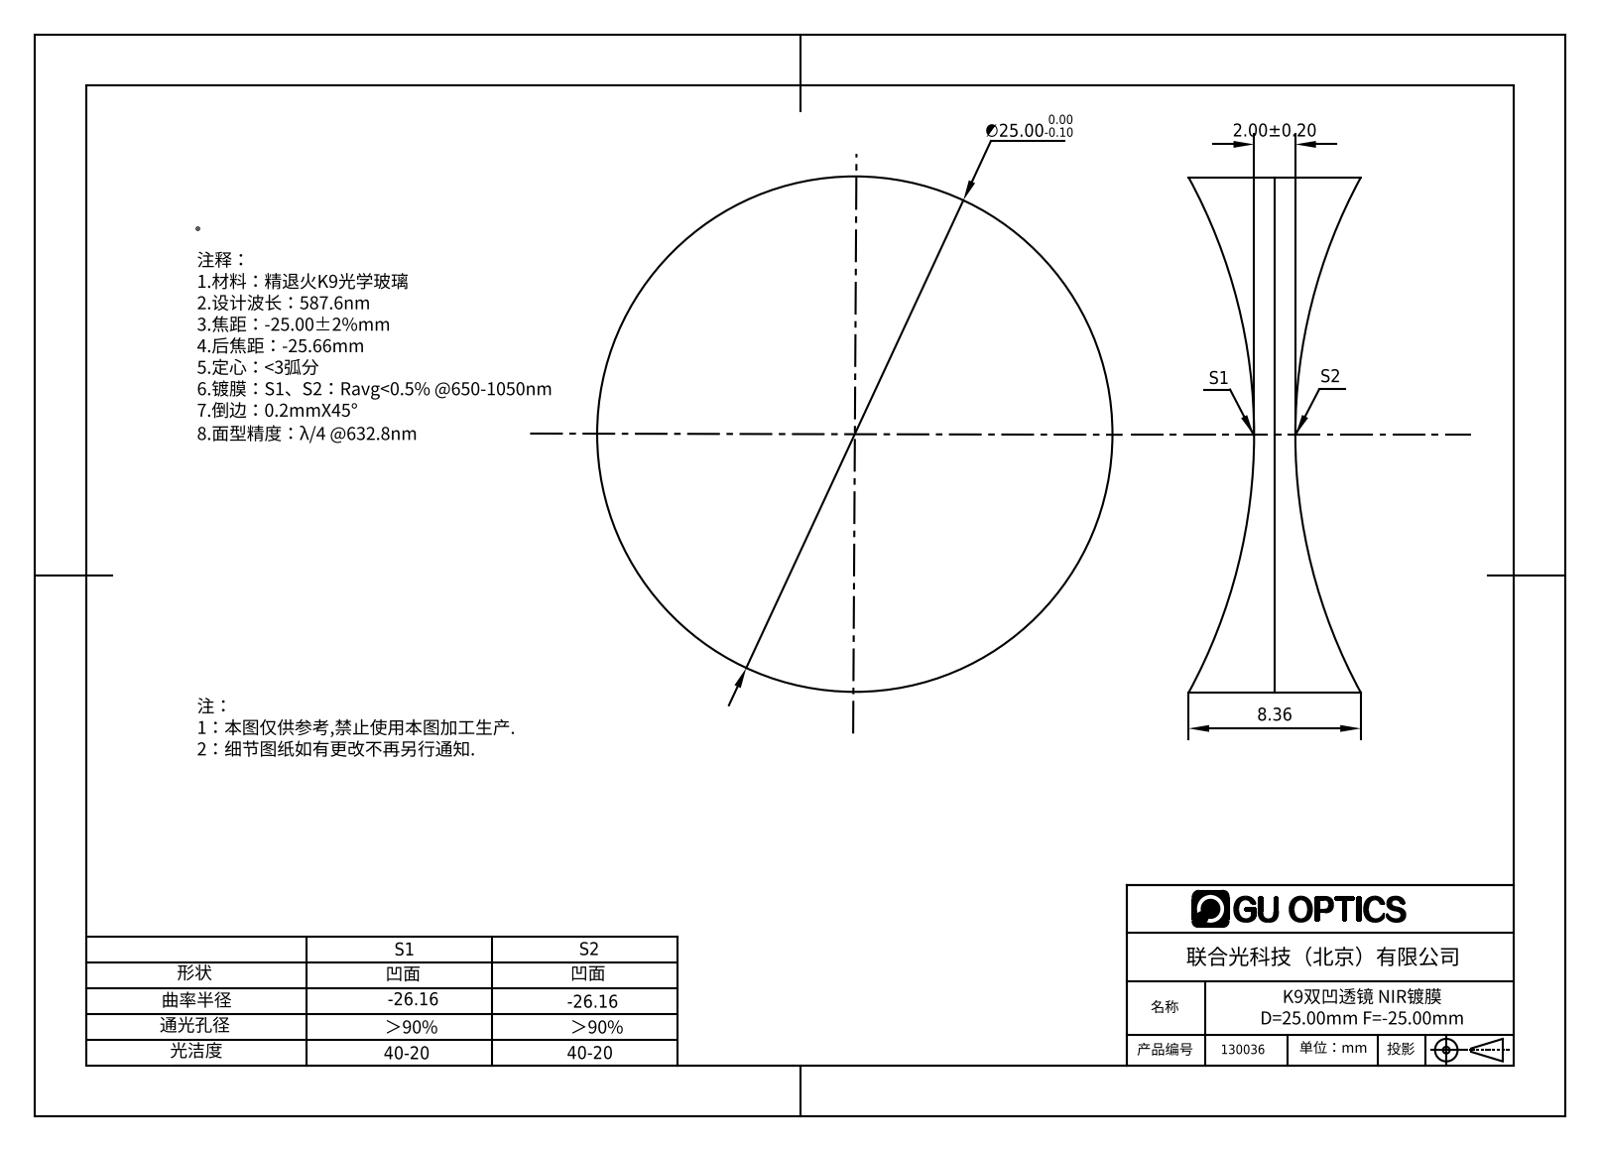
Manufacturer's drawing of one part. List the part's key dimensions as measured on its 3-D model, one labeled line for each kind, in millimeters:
Part name (STEP PRODUCT): 130010
STEP written by: SolidWorks 2016 (AUTOMOTIVE_DESIGN)
Units: millimetres
Bodies: 1 solid, 6 faces (0 planar, 2 cylindrical, 4 other)
Overall size (bounding box): 25 × 25 × 8.36
Volume: 2 509 mm³ · Surface area: 1 702 mm²
Round bosses / shafts (diameter × count): ⌀25 ×1
